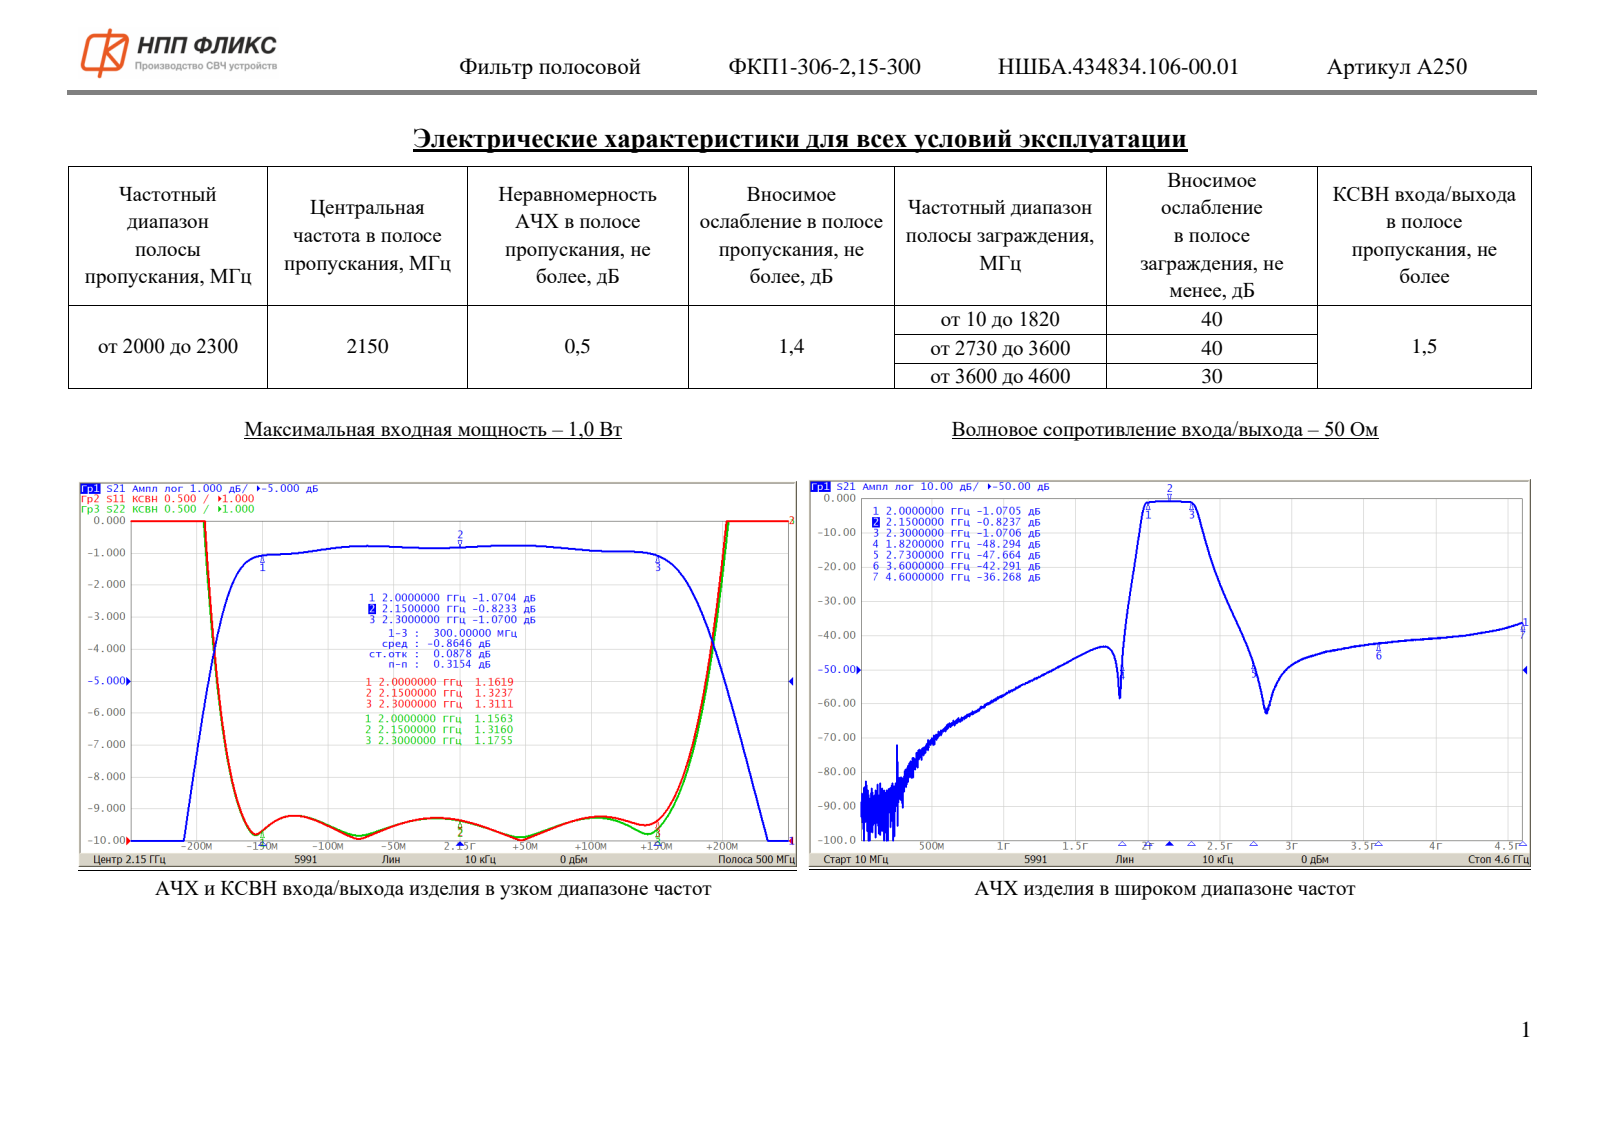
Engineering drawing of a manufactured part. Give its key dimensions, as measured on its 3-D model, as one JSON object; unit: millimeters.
{"part_name": "НШБА.434834.106-00.01_Фильтр ФКП1-306-2,15-300", "step_written_by": "ASCON Math Kernel (CONFIG_CONTROL_DESIGN)", "units": "millimeters", "bodies": {"solids": 2, "faces": 350, "planar": 219, "cylindrical": 24, "other": 107}, "overall_size": [10, 4.75, 4.3], "volume_mm3": 151, "surface_area_mm2": 358, "round_holes": [[0.6, 2], [1, 2]], "partial_cylinders_radius": [[0.9, 4], [0.2, 3], [0.3, 2], [1.2, 2], [0.1, 1], [0.35, 1], [0.6, 1]], "face_to_face_distances": [4, 3.45, 4.3, 1, 1.3, 4.45, 4.75, 10, 9.75, 3], "hole_center_spacings": [2, 4, 6]}
